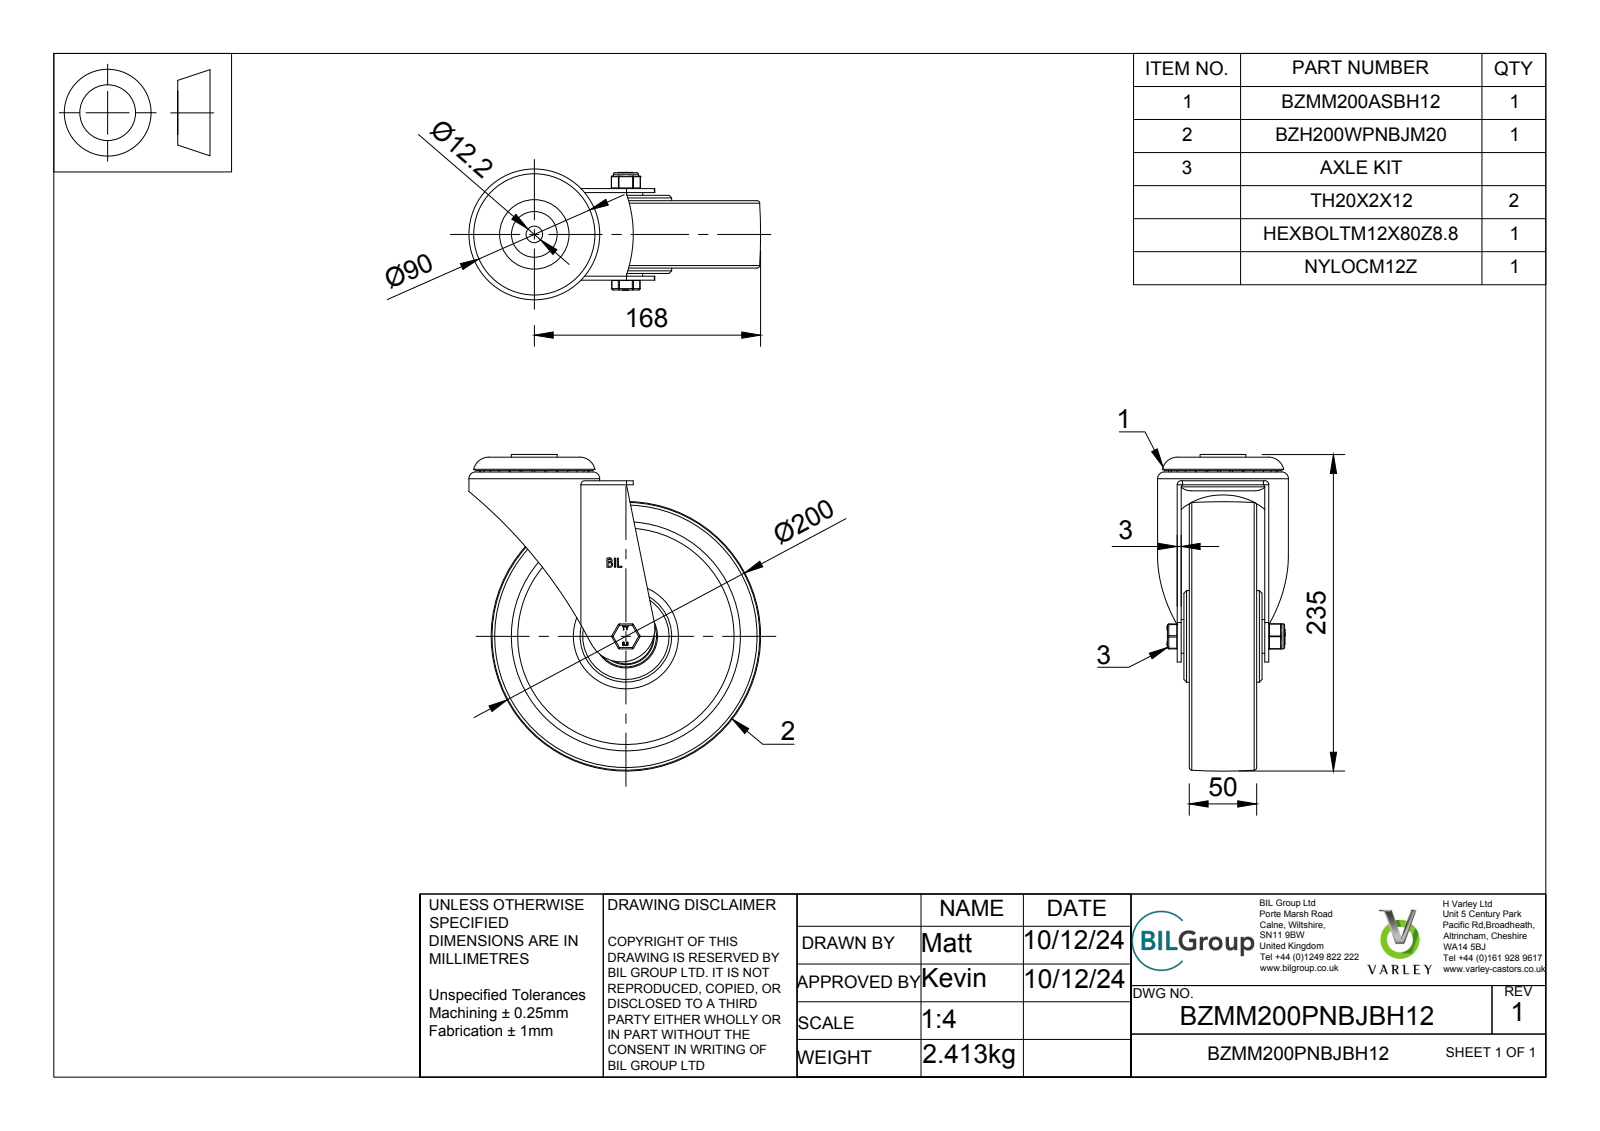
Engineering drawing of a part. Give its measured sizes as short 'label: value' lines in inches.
name: BZMM200PNBJBH12 v3; BZH200WPNBJM20 v1; BZH200WPNBJ; POLYURETHANE TYRE (+8 more)
written by: Autodesk Translation Framework v13.20.0.188 (AP242_MANAGED_MODEL_BASED_3D_ENGINEERING_MIM_LF)
unit: in
bodies: 81 solids, 1085 faces (404 planar, 193 cylindrical, 488 other)
size: 9.252 × 8.524 × 3.819
volume: 59.4 in³; area: 509.2 in²
holes: 2× ⌀0.48, 1× ⌀0.472, 1× ⌀0.484, 1× ⌀0.551, 1× ⌀0.787, 1× ⌀0.846, 1× ⌀1.122, 1× ⌀1.213, 1× ⌀1.587, 1× ⌀1.594, 1× ⌀1.634, 1× ⌀1.654
bosses: 1× ⌀3.819, 1× ⌀2.677, 1× ⌀2.48, 1× ⌀1.606, 1× ⌀1.535, 1× ⌀1.339, 1× ⌀1.232, 1× ⌀1.063
rounds: 18× R0.02, 12× R0.039, 4× R0.059, 2× R0.118, 1× R0.65, 1× R0.768, 1× R0.984, 1× R3.642
face distances: 0.118, 2.205, 0.354, 0.453, 1.211, 0.758, 0.472, 0.236, 0.994, 1.447
